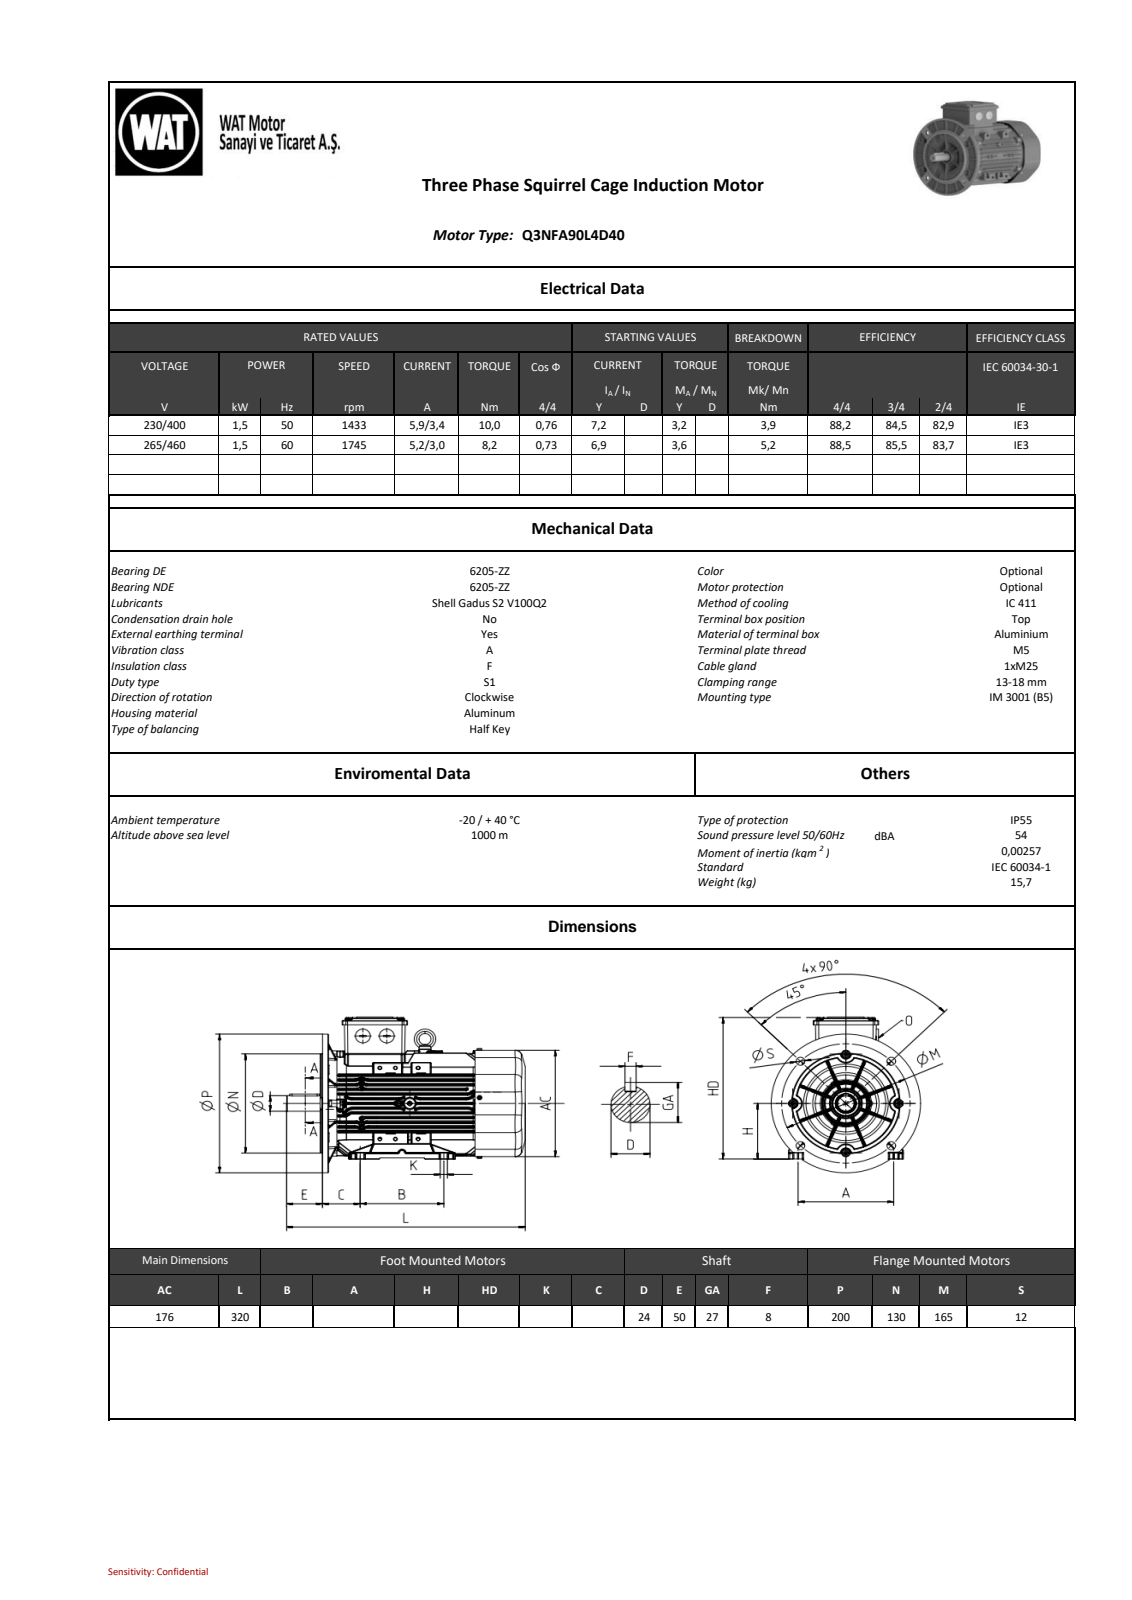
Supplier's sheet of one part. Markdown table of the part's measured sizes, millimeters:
| quantity | value |
| --- | --- |
| part name | C9012118CE057p32 |
| STEP written by | SIEMENS PLM Software NX 11.0 (AUTOMOTIVE_DESIGN) |
| units | millimeters |
| bodies | 0 solids, 17782 faces (4431 planar, 5666 cylindrical, 7685 other) |
| overall size | 320 × 220.97 × 198.95 |
| round holes (diameter × count) | 4.2 × 10, 5.1 × 10, 9 × 6, 12 × 4, 2 × 2, 2.5 × 2, 3 × 2, 7 × 2, 4 × 1, 8 × 1, 12.2 × 1, 23.9 × 1 |
| round bosses / shafts (diameter × count) | 5 × 16, 9.2 × 10, 8.5 × 10, 8 × 8, 4 × 8, 9.4 × 6, 25 × 3, 35 × 2 |
| partial cylindrical surfaces (radius × count) | 0.5 × 1446, 1 × 746, 0.8 × 563, 0.2 × 280, 0.3 × 162, 1.5 × 130, 4 × 82, 2 × 77 |
| main face-to-face distances | 4.49, 4.48, 4.5, 4.79, 4.19, 56, 4.78, 4.18, 0.8, 0.31 |
| hole center spacings | 20, 40, 81, 14.14, 14.15, 28.28, 92.93, 132.7 |
